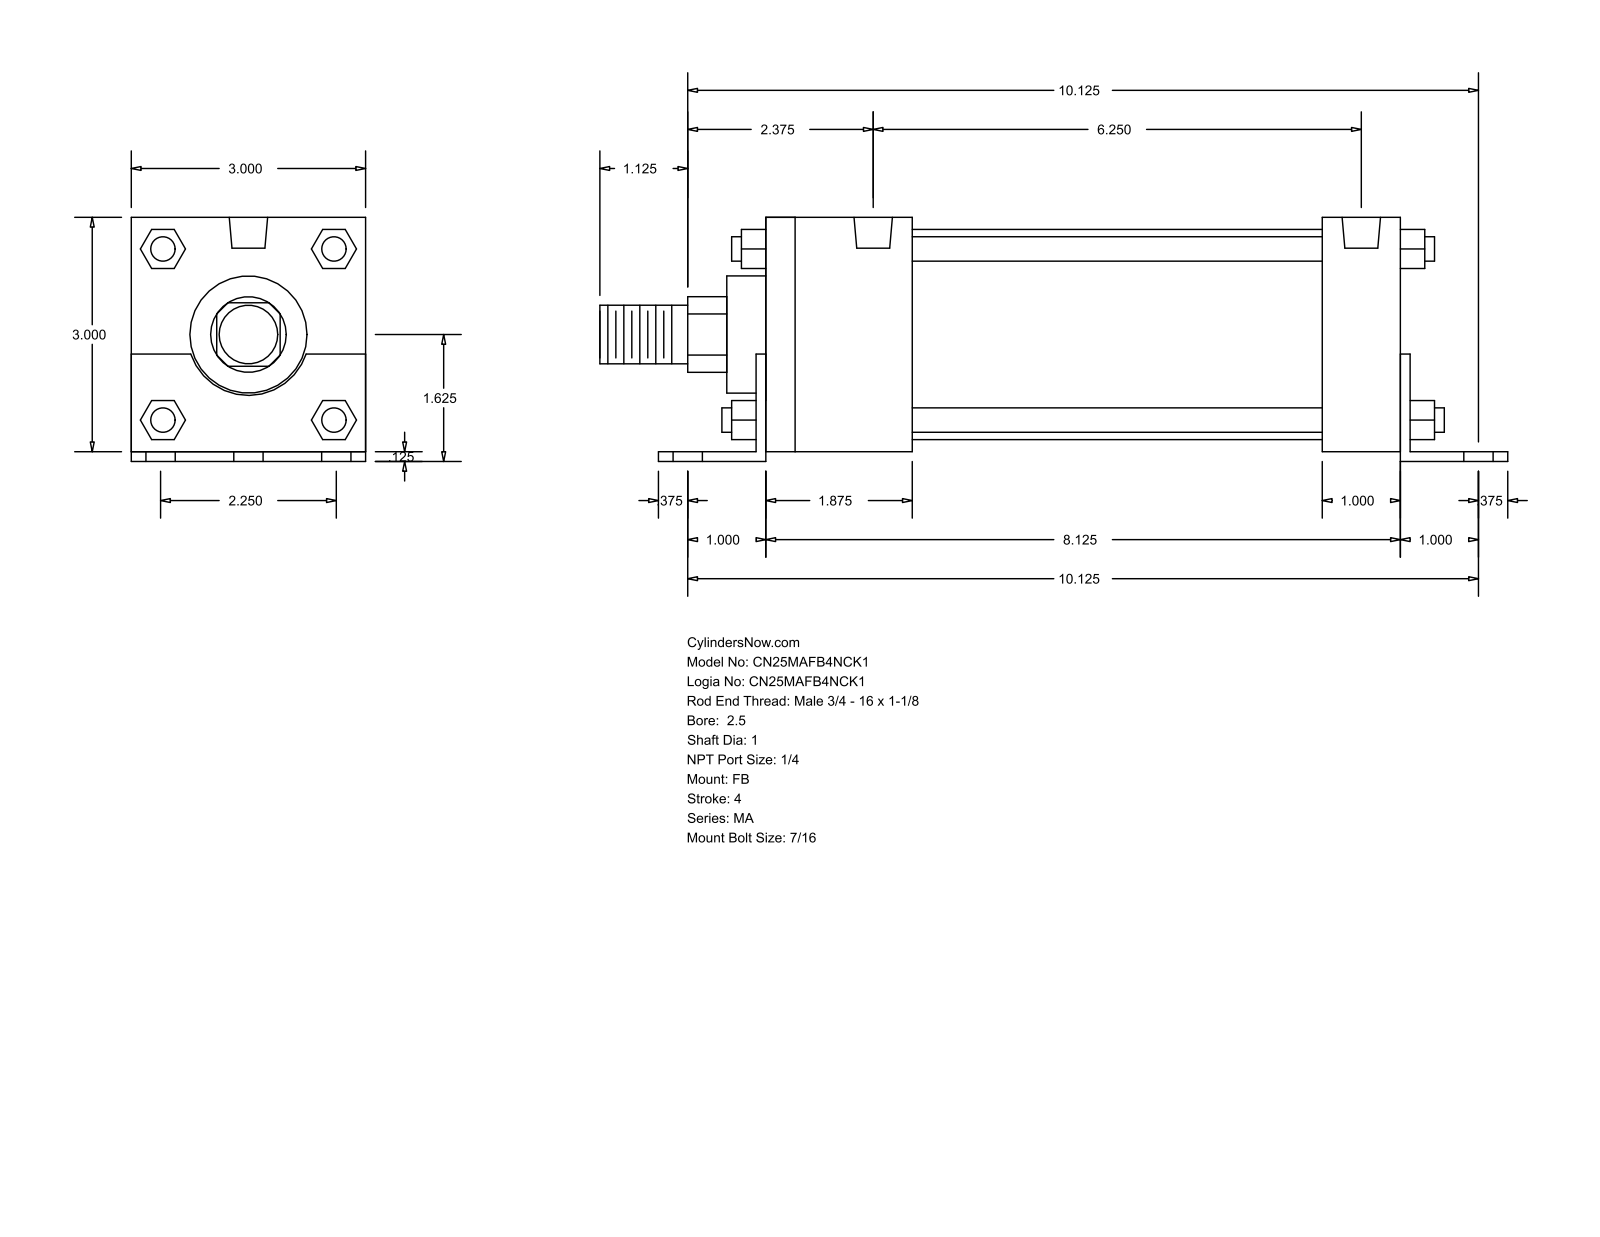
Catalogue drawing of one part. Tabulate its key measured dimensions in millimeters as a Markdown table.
| quantity | value |
| --- | --- |
| part name | MA_FB__0250_1 |
| STEP written by | GSSL Pune (CONFIG_CONTROL_DESIGN) |
| units | millimeters |
| bodies | 0 solids, 140 faces (105 planar, 35 cylindrical, 0 other) |
| overall size | 295.27 × 79.38 × 76.2 |
| round holes (diameter × count) | 11.11 × 6, 7.94 × 4, 12.49 × 2 |
| round bosses / shafts (diameter × count) | 7.94 × 4, 68.33 × 1, 38.1 × 1, 25.4 × 1, 19.05 × 1 |
| partial cylindrical surfaces (radius × count) | 12.29 × 1, 19.81 × 1 |
| main face-to-face distances | 76.2, 3.17, 79.37, 209.55, 206.38, 12.7, 28.57, 25.4, 50.8, 47.63 |
| hole center spacings | 28.57, 258.76, 257.18, 47.63, 57.14, 66.75, 158.74, 198.91 |
